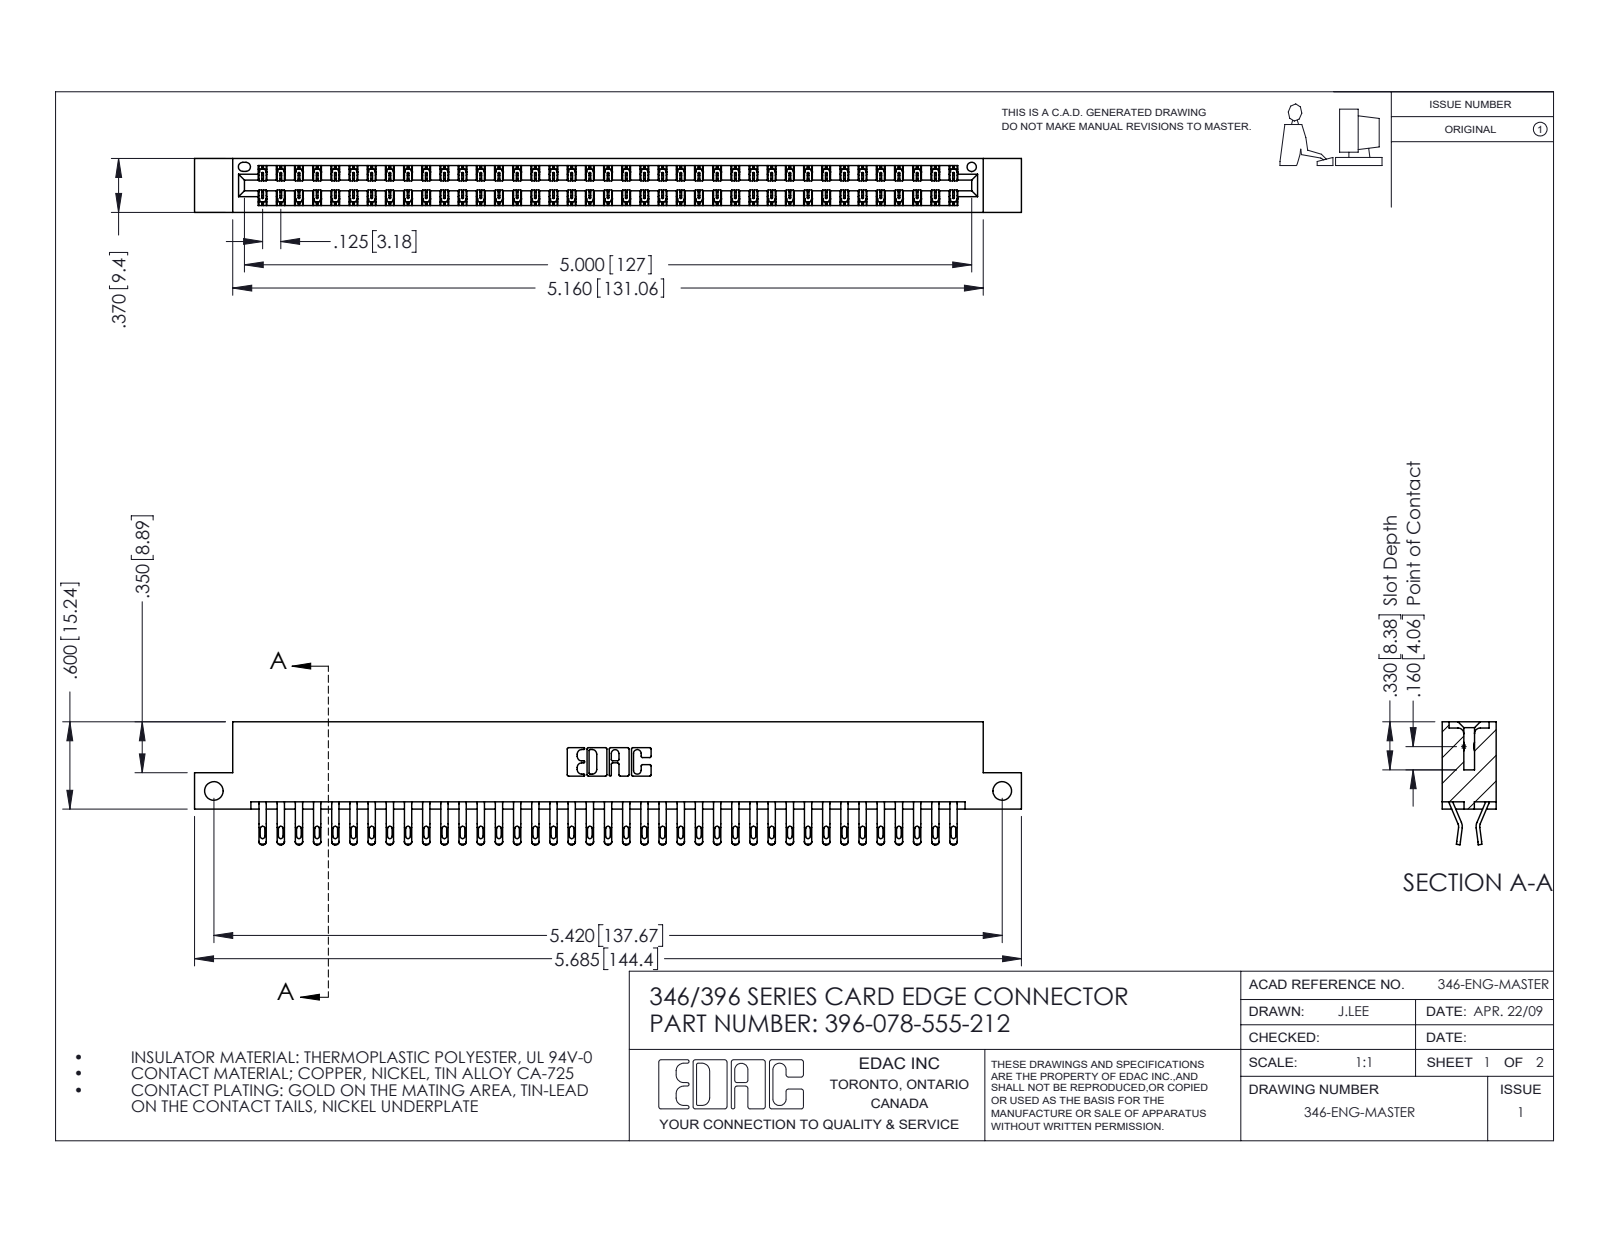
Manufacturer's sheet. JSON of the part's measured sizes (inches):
{"part_name": "346 Part_Flush Mounting Lugs - Side Mount; 345-292-001_555 Tail; 396-078-555-212", "step_written_by": "SolidWorks 2016 (CONFIG_CONTROL_DESIGN)", "units": "inches", "bodies": {"solids": 79, "faces": 4646, "planar": 2650, "cylindrical": 1996, "other": 0}, "overall_size": [5.685, 0.845, 0.37], "volume_in3": 0.866, "surface_area_in2": 31.21, "round_holes": [[0.128, 2], [0.064, 1]], "partial_cylinders_radius": [[0.016, 156], [0.02, 156], [0.006, 117], [0.01, 22], [0.007, 6], [0.031, 6], [0.026, 3], [0.01, 2]], "face_to_face_distances": [0.048, 0.322, 0.37, 0.25, 0.025, 0.072, 0.298, 0.275, 0.148, 0.222], "hole_center_spacings": [5.42]}
